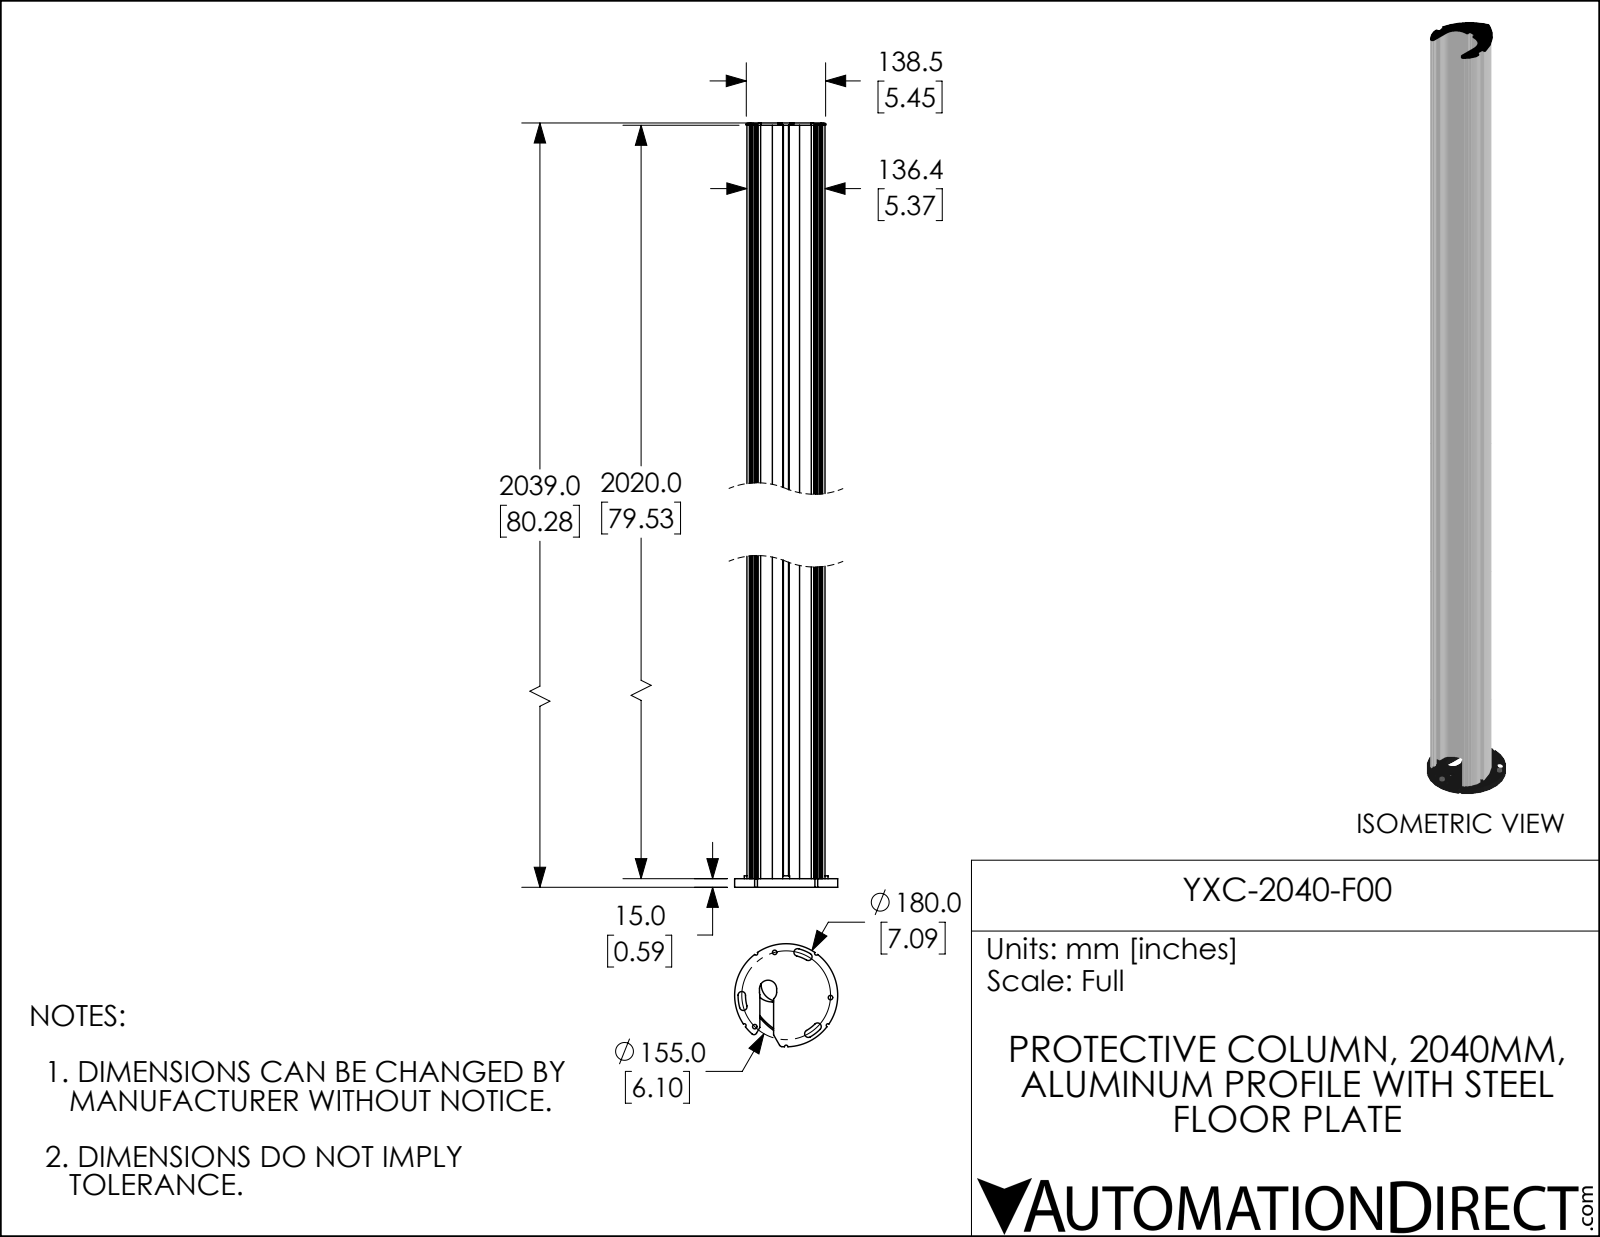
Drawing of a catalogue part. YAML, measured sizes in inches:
part_name: "YXC-2040-F00"
step_written_by: "SolidWorks 2019 (AUTOMOTIVE_DESIGN)"
units: inches
bodies: {solids: 1, faces: 326, planar: 201, cylindrical: 112, other: 13}
overall_size: [80.276, 7.087, 7.085]
volume: 716.2
surface_area: 2430
round_holes:
  - {diameter: 0.307, count: 3}
  - {diameter: 0.173, count: 1}
  - {diameter: 0.591, count: 1}
round_bosses_or_shafts:
  - {diameter: 0.472, count: 3}
  - {diameter: 0.291, count: 2}
  - {diameter: 7.087, count: 1}
partial_cylinders:
  - {radius: 0.118, count: 17}
  - {radius: 0.039, count: 6}
  - {radius: 0.051, count: 6}
  - {radius: 0.256, count: 6}
  - {radius: 0.591, count: 4}
  - {radius: 0.197, count: 3}
  - {radius: 0.236, count: 3}
  - {radius: 0.059, count: 2}
face_to_face_distances: [0.453, 0.118, 4.916, 0.775, 4.594, 0.322, 4.141, 0.335, 5.034, 0.44]
hole_center_spacings: [1.255, 1.257, 3.717, 3.719, 4.656, 4.659, 4.937, 5.285]
